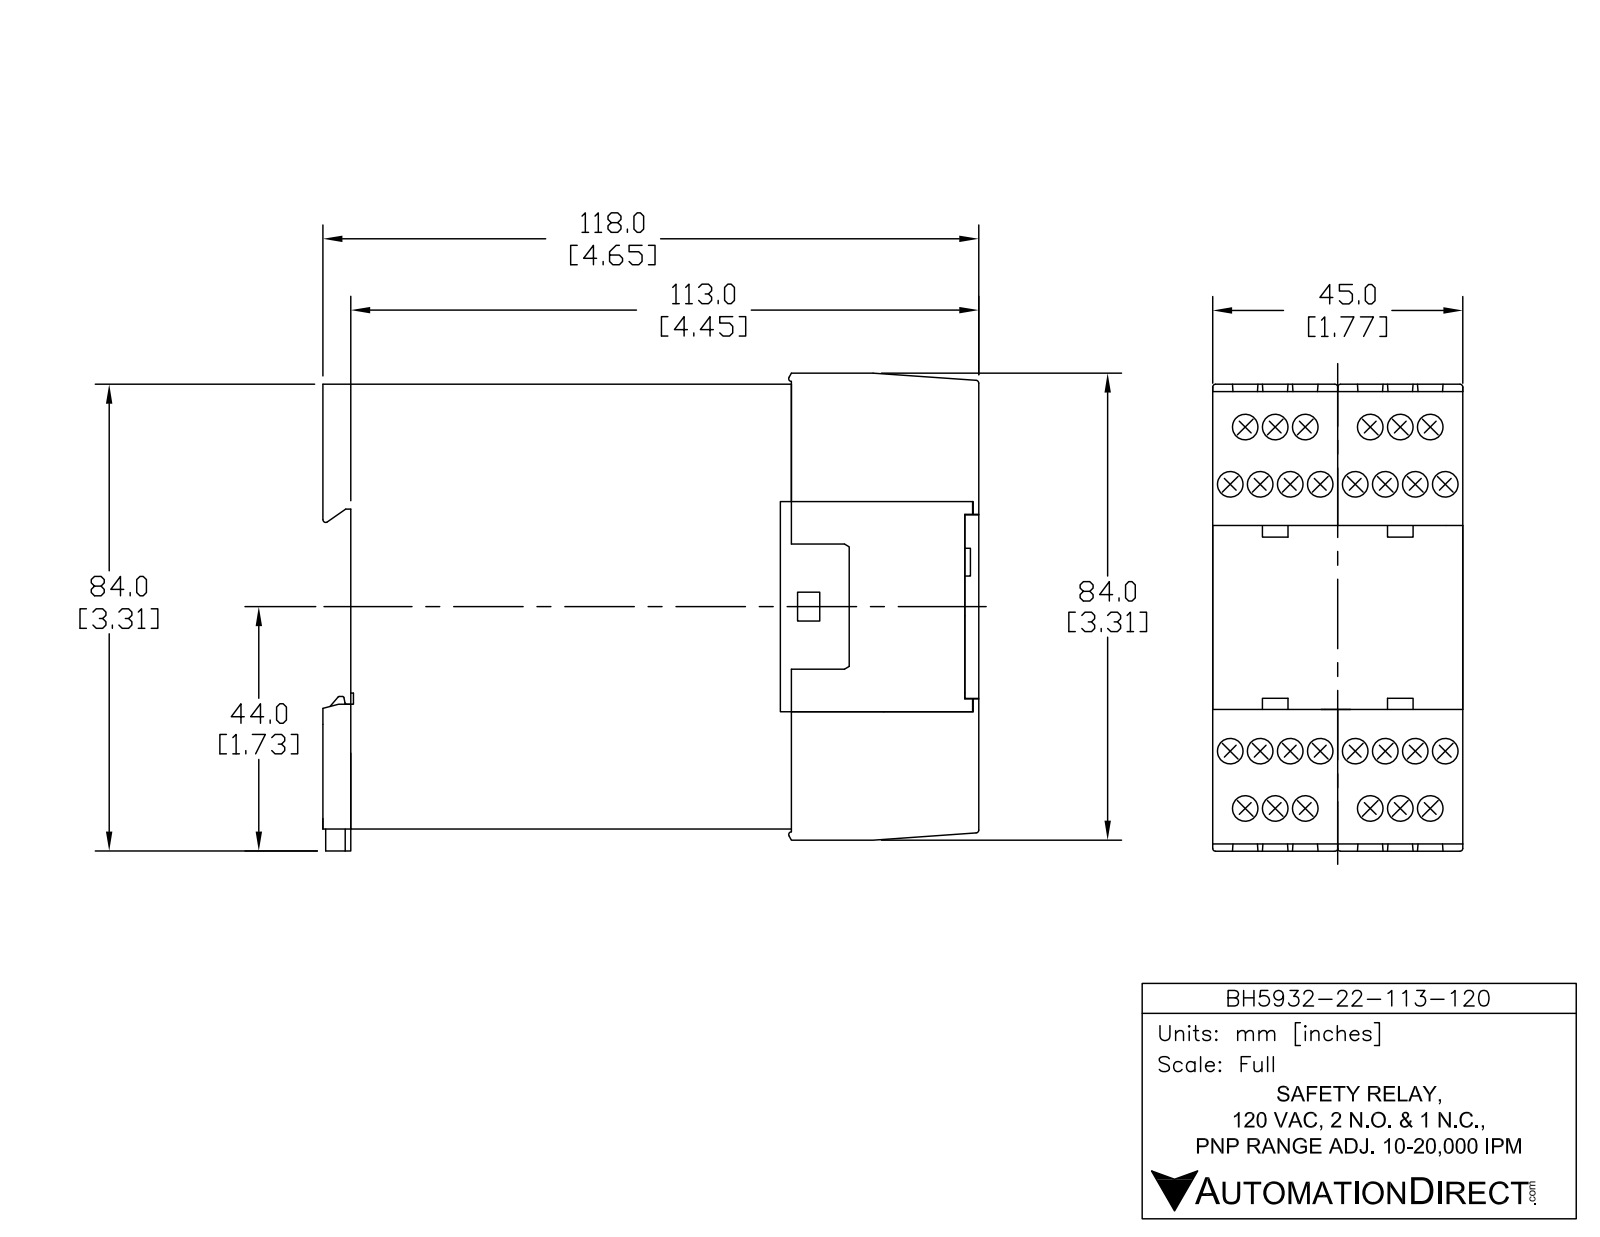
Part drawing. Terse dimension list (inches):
name: BH5932-22-113-120
written by: SolidWorks 2017 (AUTOMOTIVE_DESIGN)
unit: in
bodies: 1 solid, 1533 faces (1034 planar, 369 cylindrical, 130 other)
size: 4.654 × 3.346 × 1.772
volume: 24.87 in³; area: 74.68 in²
holes: 28× ⌀0.181, 2× ⌀0.315
bosses: 1× ⌀0.087
rounds: 133× R0.02, 64× R0.008, 32× R0.059, 8× R0.049, 3× R0.079, 2× R0.012, 1× R0.043, 1× R0.085
face distances: 1.772, 3.15, 1.77, 4.449, 0.079, 3.071, 1.768, 0.037, 2.992, 0.884
hole spacings: 0.419, 2.306, 0.213, 0.516, 2.325, 0.886, 0.425, 0.879
